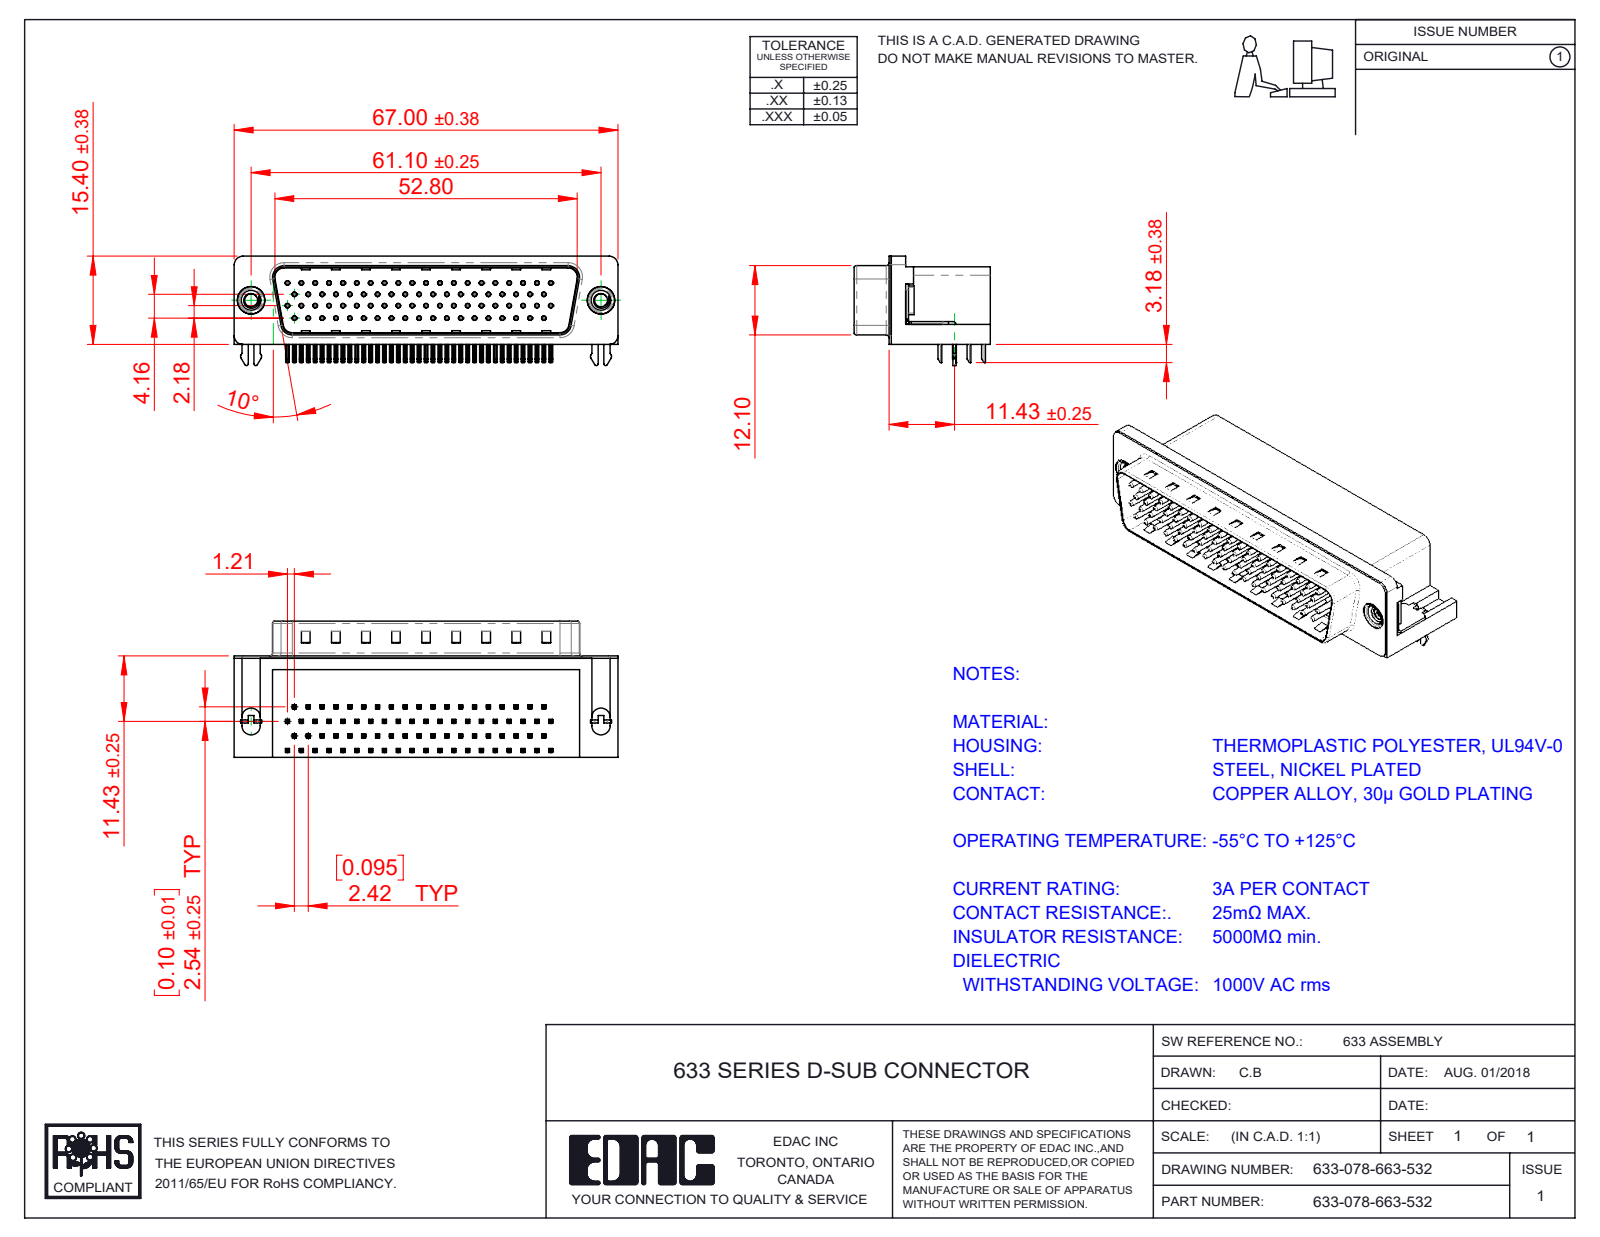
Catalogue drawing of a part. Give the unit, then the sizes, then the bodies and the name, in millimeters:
Units: millimetres
Overall size (bounding box): 67 × 23.8 × 19.1
Round holes (diameter × count): ⌀0.35 ×78, ⌀0.8 ×78, ⌀2.26 ×2, ⌀4 ×2, ⌀4.8 ×2, ⌀5 ×2
Round bosses / shafts (diameter × count): ⌀0.75 ×78, ⌀4.9 ×2, ⌀4.75 ×2, ⌀3.9 ×2
Partial cylindrical surfaces — rounded edges, fillets, slot ends (radius × count): R0.25 ×320, R0.12 ×156, R1 ×16, R0.5 ×14, R1.6 ×8, R1.5 ×6, R0.32 ×4, R0.45 ×4
Main face-to-face distances: 0.4, 13.2, 17.3, 11.7, 13.35, 2.05, 13.75, 1.65, 1.85, 11.9
Hole centre spacings: 2.42, 4.84, 7.26, 9.68, 6.26, 7.13, 12.1, 8.62
Volume: 14 614 mm³ · Surface area: 16 358 mm²
Bodies: 84 solids, 6316 faces (4013 planar, 1786 cylindrical, 517 other)
Part name (STEP PRODUCT): 633 Shell_78 Contact; 633 Contact Bottom_78 Contact; 633 Housing_78 Contact; 633-078-663-532 (+5 more)
STEP written by: SolidWorks 2016 (CONFIG_CONTROL_DESIGN)
